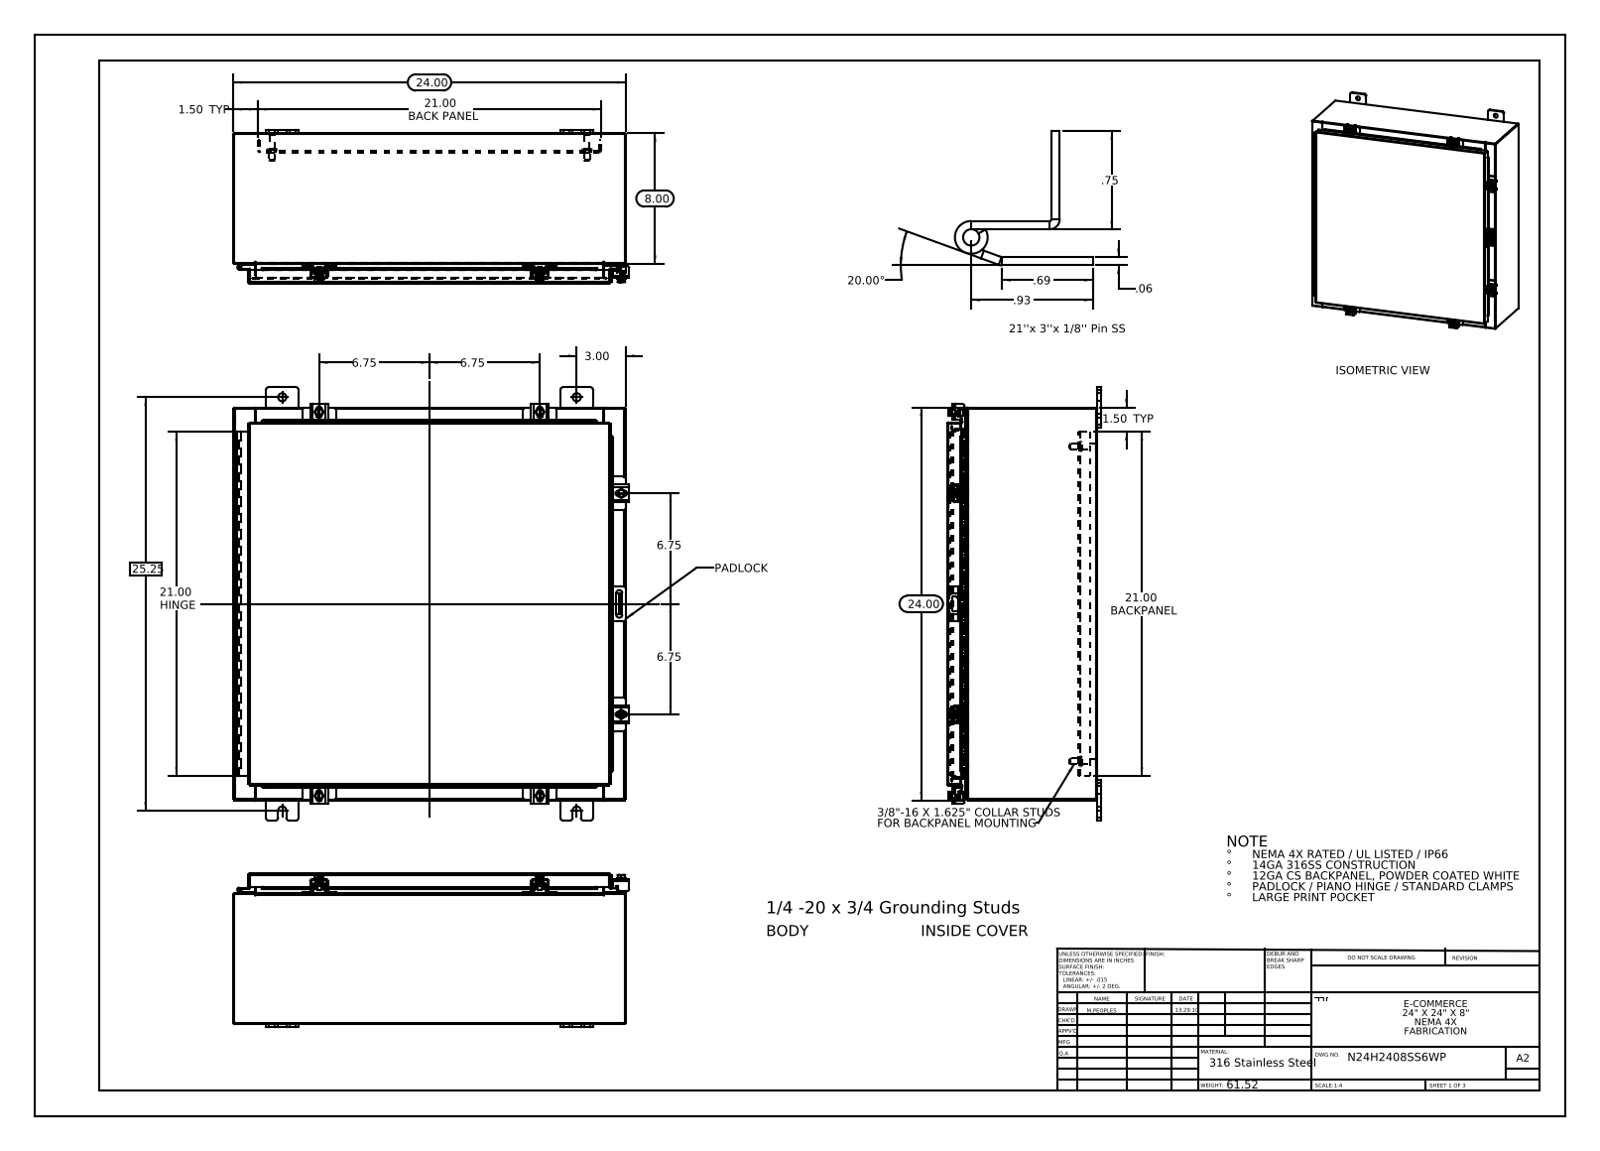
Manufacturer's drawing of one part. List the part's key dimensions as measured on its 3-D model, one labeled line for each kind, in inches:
Part name (STEP PRODUCT): N24H2408SS6WP Mounting Studs; N24H2408SS6WP Mounting Feet; N24H2408SS6WP Padlock Hasp; N24H2408SS6WP Bottom (+8 more)
STEP written by: SolidWorks 2013 (CONFIG_CONTROL_DESIGN)
Units: inches
Bodies: 47 solids, 1709 faces (908 planar, 705 cylindrical, 96 other)
Overall size (bounding box): 26.5 × 24.211 × 9.389
Volume: 216.2 in³ · Surface area: 5 431 in²
Round holes (diameter × count): ⌀0.5 ×8, ⌀0.213 ×6, ⌀0.26 ×6, ⌀0.125 ×2
Round bosses / shafts (diameter × count): ⌀0.25 ×7, ⌀0.5 ×6, ⌀0.399 ×6, ⌀0.625 ×4, ⌀0.375 ×4, ⌀0.33 ×4
Partial cylindrical surfaces — rounded edges, fillets, slot ends (radius × count): R0.06 ×30, R0.013 ×25, R0.19 ×24, R0.088 ×21, R0.12 ×12, R0.141 ×12, R0.125 ×10, R0.05 ×9
Main face-to-face distances: 0.075, 9.126, 23.925, 9.201, 9.051, 0.104, 1, 1.075, 8.051, 8.126
Hole centre spacings: 16.509, 19.134, 21.544, 26.907, 13.5, 1.858, 2.277, 2.423
